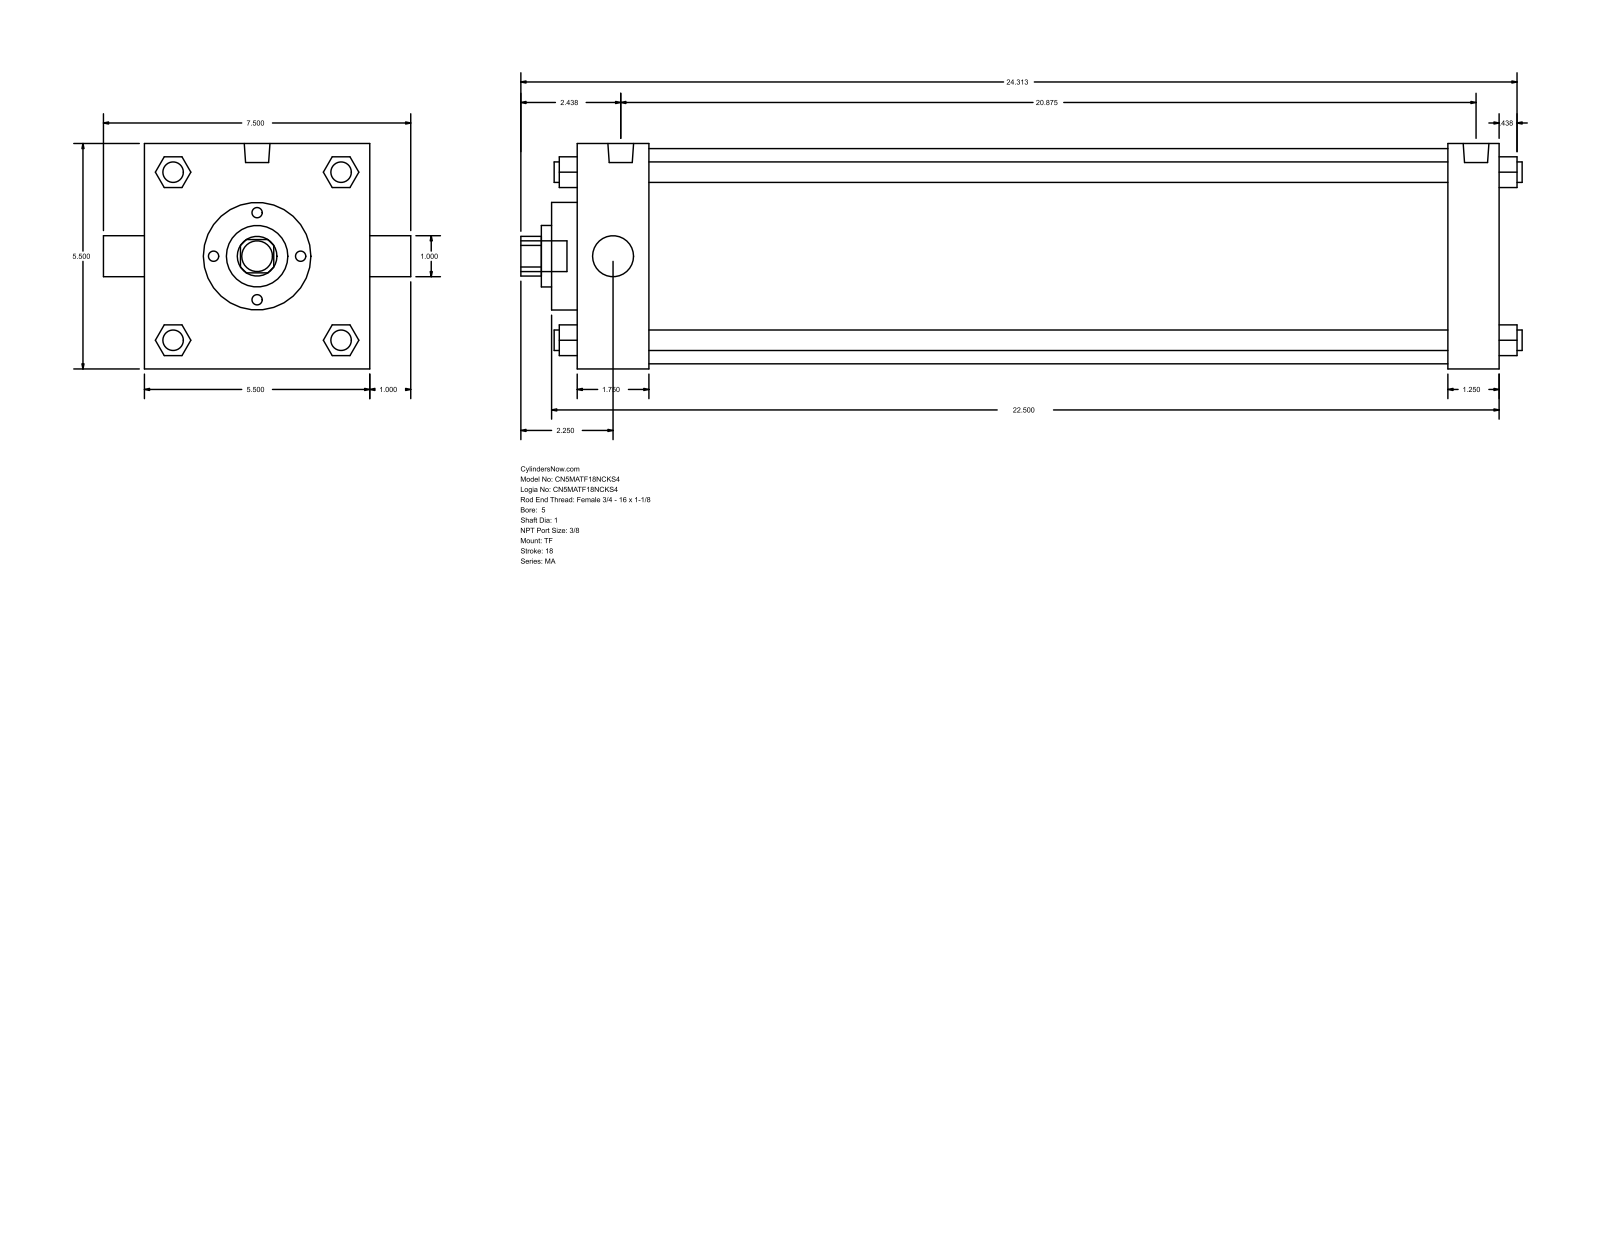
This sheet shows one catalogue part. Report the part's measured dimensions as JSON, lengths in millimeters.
{"part_name": "MA_TF__0500_1", "step_written_by": "GSSL Pune (CONFIG_CONTROL_DESIGN)", "units": "millimeters", "bodies": {"solids": 0, "faces": 122, "planar": 93, "cylindrical": 29, "other": 0}, "overall_size": [620.71, 190.5, 139.7], "round_holes": [[25.4, 2], [38.1, 1], [66.67, 1], [133.35, 1]], "round_bosses_or_shafts": [[12.7, 4], [11.11, 3], [15.93, 2], [19.05, 1]], "partial_cylinders_radius": [[12.29, 1]], "face_to_face_distances": [139.7, 571.5, 539.75, 31.75, 44.46, 495.29, 527.04, 15.87, 60.33, 555.62]}
